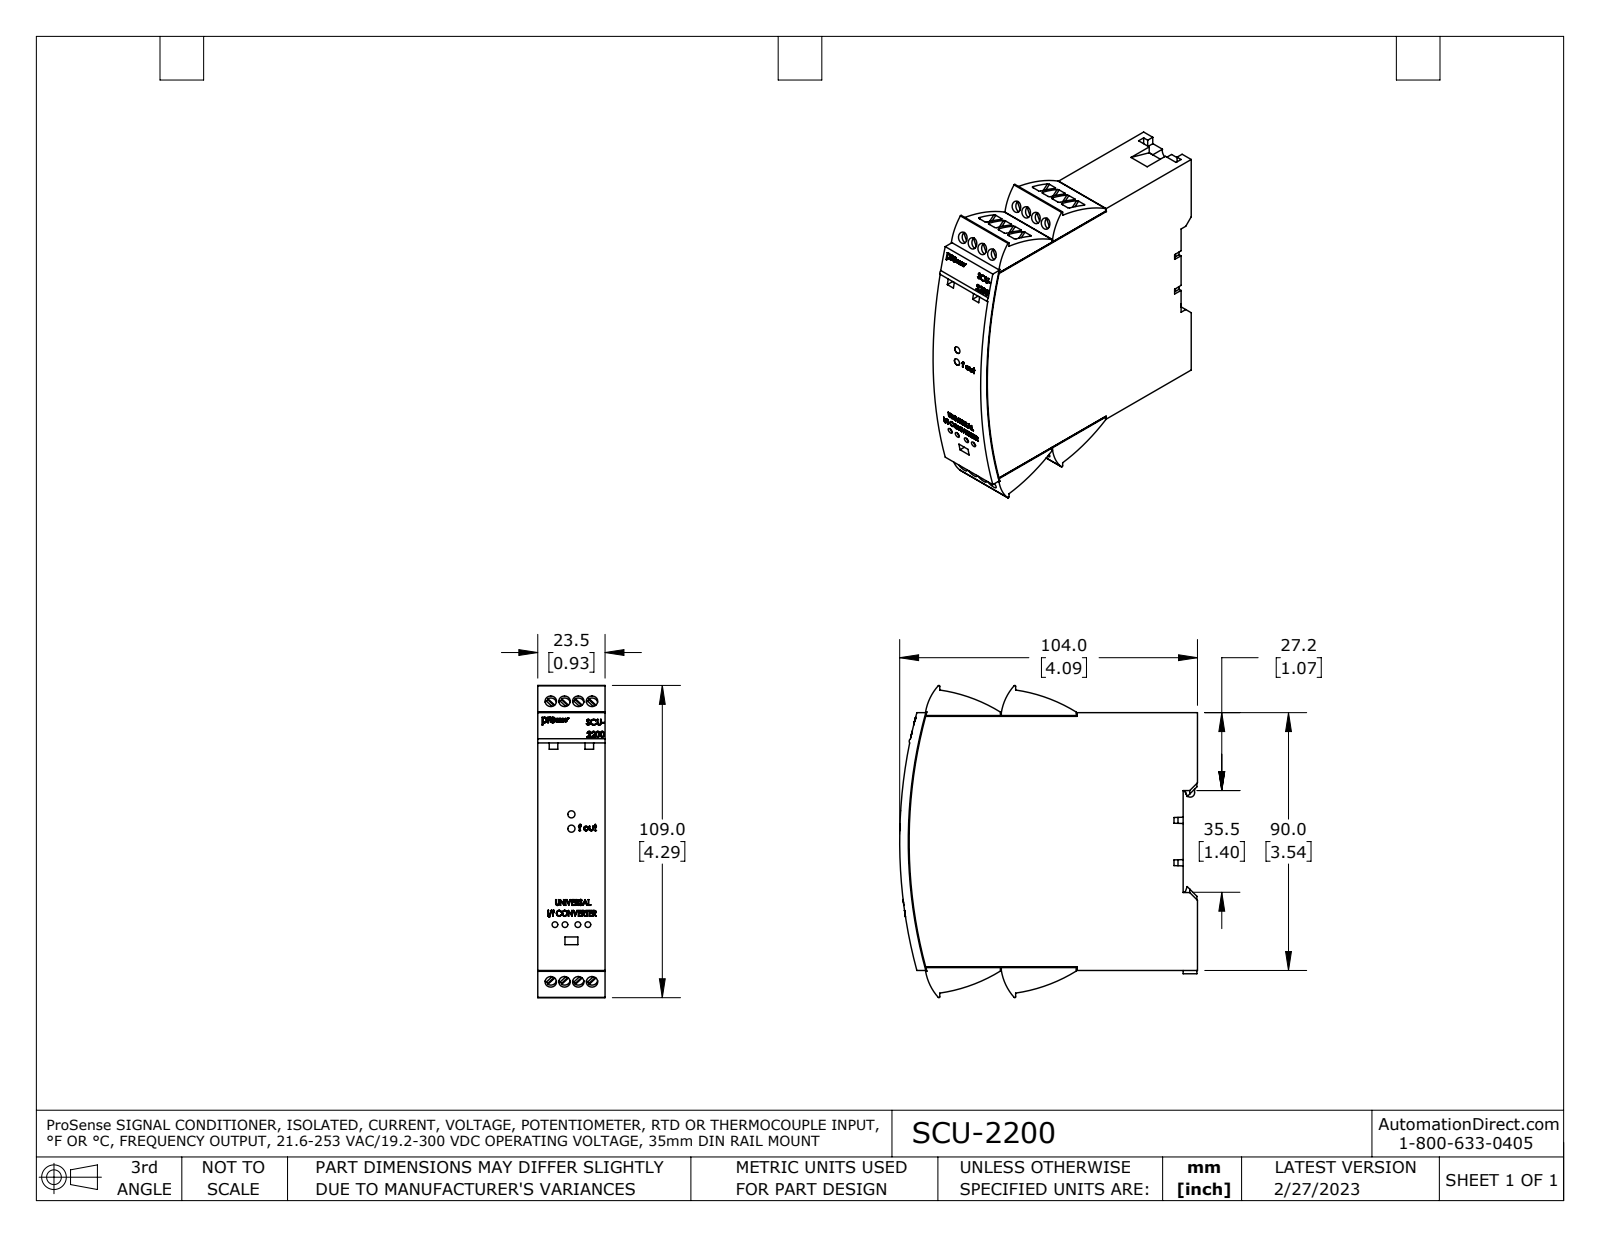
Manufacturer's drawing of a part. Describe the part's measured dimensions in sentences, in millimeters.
The part is named "SCU-2200 from 4000_6000_9000 Complete asm nc m1E FP MOD1 fxt". Its 3-D file was written by "SolidWorks 2021 (AUTOMOTIVE_DESIGN)". It is 3 solids with 1180 faces: 693 planar, 232 cylindrical and 255 other. Overall it measures 109 by 104 by 23.5 millimeters. Its volume is 218 900 cubic millimeters and its surface area 35 770 square millimeters. Round holes: 16 of diameter 4, 4 of diameter 2, 4 of diameter 2.3, 2 of diameter 2.5. Round bosses or shafts: 2 of diameter 2. Partial cylindrical surfaces (rounded edges, fillets, slot ends): 69 of radius 0.5, 4 of radius 0.3, 4 of radius 1, 4 of radius 18.4, 4 of radius 55.2, 3 of radius 1.5, 3 of radius 2.5, 2 of radius 0.8. The main face-to-face distances are 23.5, 90, 2.5, 4.8, 4.7, 1.8, 5, 3, 2.3, 1.5. The hole center spacings are 4.8, 11, 9.6, 9.9, 13.8, 14.4, 17.5, 3.5.
